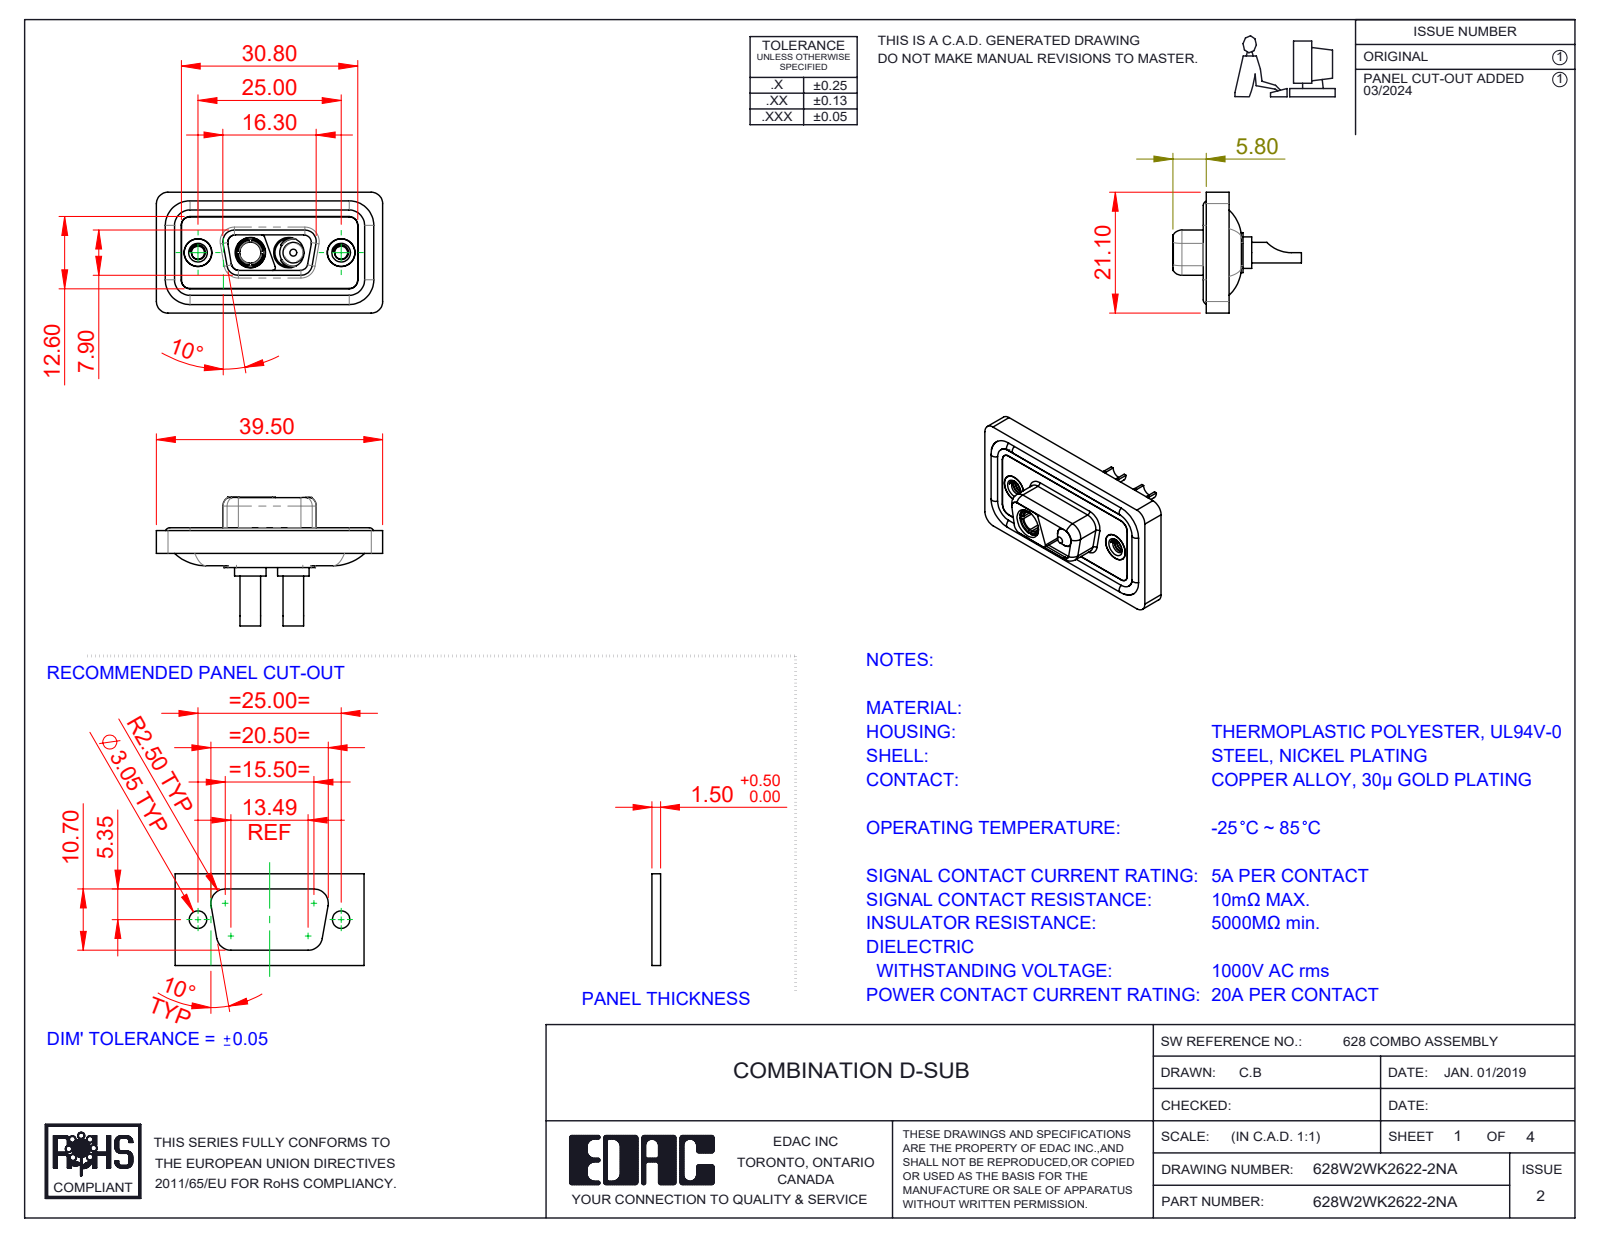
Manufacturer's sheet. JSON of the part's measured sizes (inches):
{"part_name": "628Combo Waterproof Housing_09 Contacts; 628Combo Shell Rear_09 Contacts; Power Socket_20A SC; 628W2WK2622-2NA (+4 more)", "step_written_by": "SolidWorks 2023 (CONFIG_CONTROL_DESIGN)", "units": "inches", "bodies": {"solids": 11, "faces": 510, "planar": 150, "cylindrical": 239, "other": 121}, "overall_size": [1.555, 0.884, 0.831], "volume_in3": 0.283, "surface_area_in2": 11.63, "round_holes": [[0.191, 4], [0.089, 2], [0.106, 2], [0.157, 2], [0.159, 2], [0.197, 2], [0.209, 2], [0.146, 1]], "round_bosses_or_shafts": [[0.063, 4], [0.217, 2], [0.205, 2], [0.195, 2], [0.189, 2], [0.187, 2], [0.148, 2], [0.142, 2]], "partial_cylinders_radius": [[0.059, 22], [0.079, 18], [0.053, 8], [0.063, 8], [0.02, 6], [0.01, 4], [0.024, 4], [0.026, 4]], "face_to_face_distances": [0.016, 0.043, 0.114, 0.063, 0.02, 0.071, 0.222, 0.059, 0.211, 0.122], "hole_center_spacings": [0.36, 0.624, 0.265, 0.984]}
